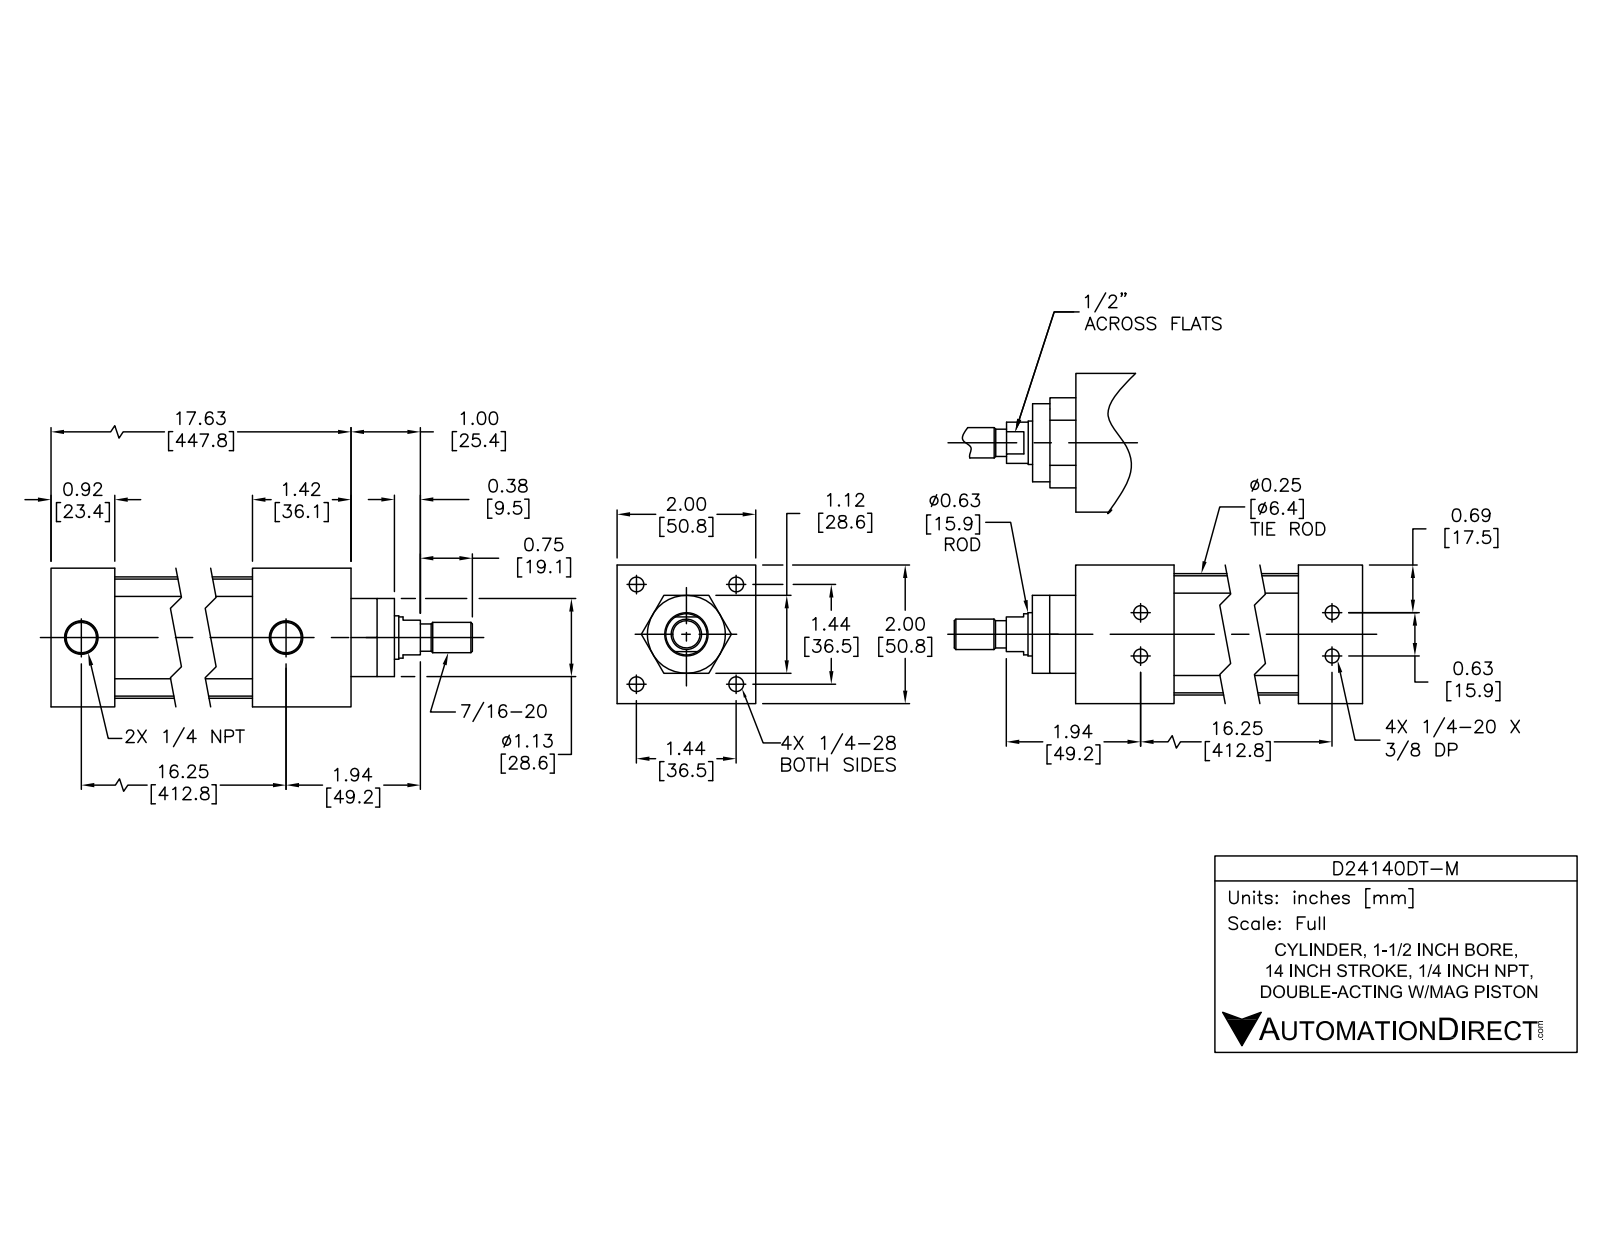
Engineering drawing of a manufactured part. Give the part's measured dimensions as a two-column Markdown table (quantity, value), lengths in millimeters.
| quantity | value |
| --- | --- |
| part name | D24140DT-M PISTON; D24140DT-M BODY; D24140DT-M |
| STEP written by | SolidWorks 2015 (AUTOMOTIVE_DESIGN) |
| units | millimeters |
| bodies | 12 solids, 303 faces (99 planar, 114 cylindrical, 90 other) |
| overall size | 492 × 50.8 × 50.8 |
| volume | 459 500 mm³ |
| surface area | 195 100 mm² |
| round holes (diameter × count) | 5 × 4, 5.4 × 4, 7.1 × 4, 10.3 × 4, 7.5 × 2, 12.1 × 2, 15.9 × 1, 16 × 1, 38.1 × 1 |
| round bosses / shafts (diameter × count) | 9.9 × 4, 6.4 × 4, 5.6 × 4, 44.5 × 1, 38 × 1, 28.5 × 1, 15.8 × 1, 15 × 1 |
| partial cylindrical surfaces (radius × count) | 5.1 × 4 |
| main face-to-face distances | 50.8, 2, 386.1, 447.6, 36.1, 411.5, 424.2, 388.1, 23.4, 28.5 |
| hole center spacings | 412.7, 7.9, 8, 15.9, 25.8, 25.8, 36.4, 36.4 |
